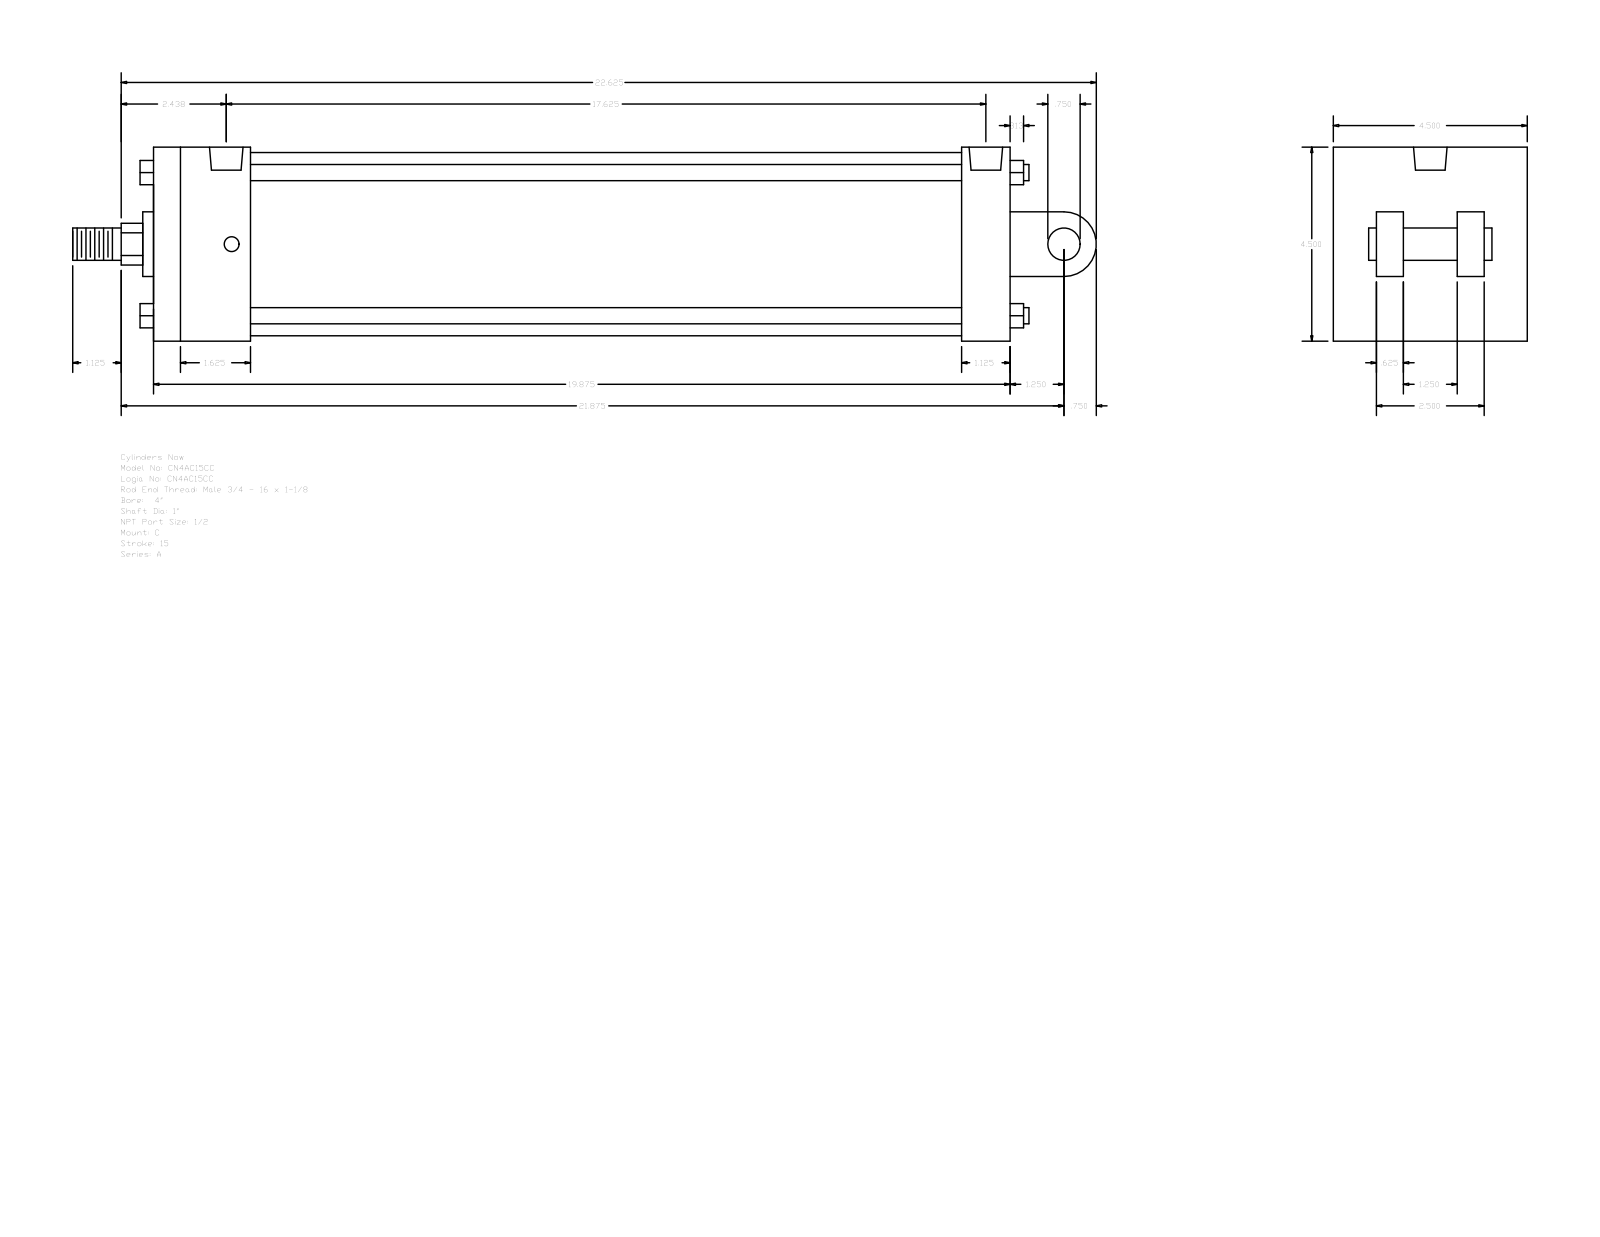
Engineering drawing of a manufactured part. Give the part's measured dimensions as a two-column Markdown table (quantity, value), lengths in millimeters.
| quantity | value |
| --- | --- |
| part name | A_C__0400_1 |
| STEP written by | GSSL Pune (CONFIG_CONTROL_DESIGN) |
| units | millimeters |
| bodies | 0 solids, 135 faces (102 planar, 33 cylindrical, 0 other) |
| overall size | 603.25 × 114.3 × 114.3 |
| round holes (diameter × count) | 8.73 × 4, 19.77 × 2 |
| round bosses / shafts (diameter × count) | 9.53 × 4, 19.05 × 2, 107.95 × 1, 38.1 × 1, 25.4 × 1 |
| partial cylindrical surfaces (radius × count) | 12.29 × 1, 19.05 × 1 |
| main face-to-face distances | 114.3, 504.83, 73.03, 476.25, 28.58, 57.15, 419.1, 447.68, 41.27, 38.1 |
| hole center spacings | 3.18, 441.32, 444.5, 447.68 |
